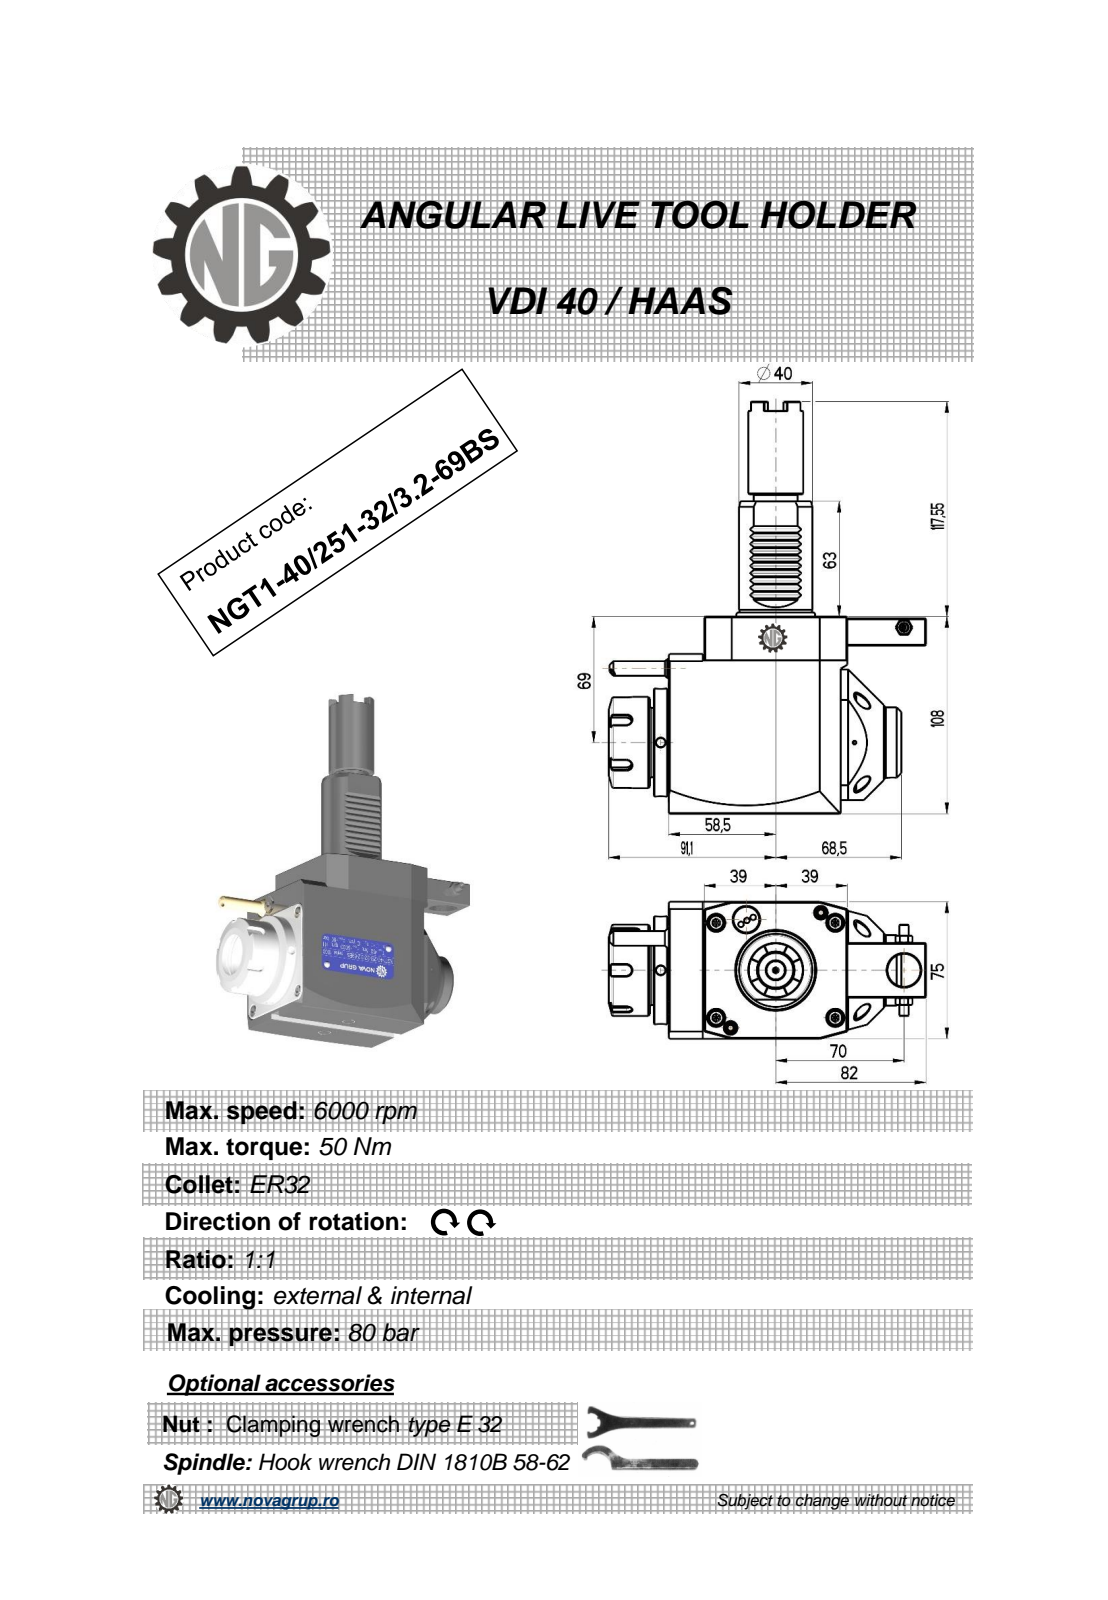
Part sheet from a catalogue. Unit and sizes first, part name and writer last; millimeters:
Units: millimetres
Overall size (bounding box): 225.55 × 173.1 × 75
Round holes (diameter × count): ⌀5 ×3, ⌀3 ×1, ⌀4.2 ×1, ⌀9.5 ×1, ⌀18 ×1, ⌀27 ×1, ⌀46 ×1
Round bosses / shafts (diameter × count): ⌀59 ×1, ⌀50 ×1, ⌀46 ×1, ⌀41 ×1, ⌀40 ×1, ⌀38.5 ×1, ⌀30 ×1, ⌀24 ×1
Partial cylindrical surfaces — rounded edges, fillets, slot ends (radius × count): R0.26 ×12, R0.3 ×10, R0.2 ×6, R3 ×5, R5.8 ×2, R6 ×2, R600 ×2, R0.5 ×1
Main face-to-face distances: 75, 108, 19.5, 27.5, 1, 3.5, 20, 83.5, 8, 22.5
Hole centre spacings: 27.34, 44.12, 61.5, 132.75, 146.94
Volume: 998 472 mm³ · Surface area: 83 953 mm²
Bodies: 1 solid, 484 faces (239 planar, 99 cylindrical, 146 other)
Part name (STEP PRODUCT): NGT1_40_251_32_3_2_69BS
STEP written by: PRO/ENGINEER BY PARAMETRIC TECHNOLOGY CORPORATION, 2010280 (CONFIG_CONTROL_DESIGN)
